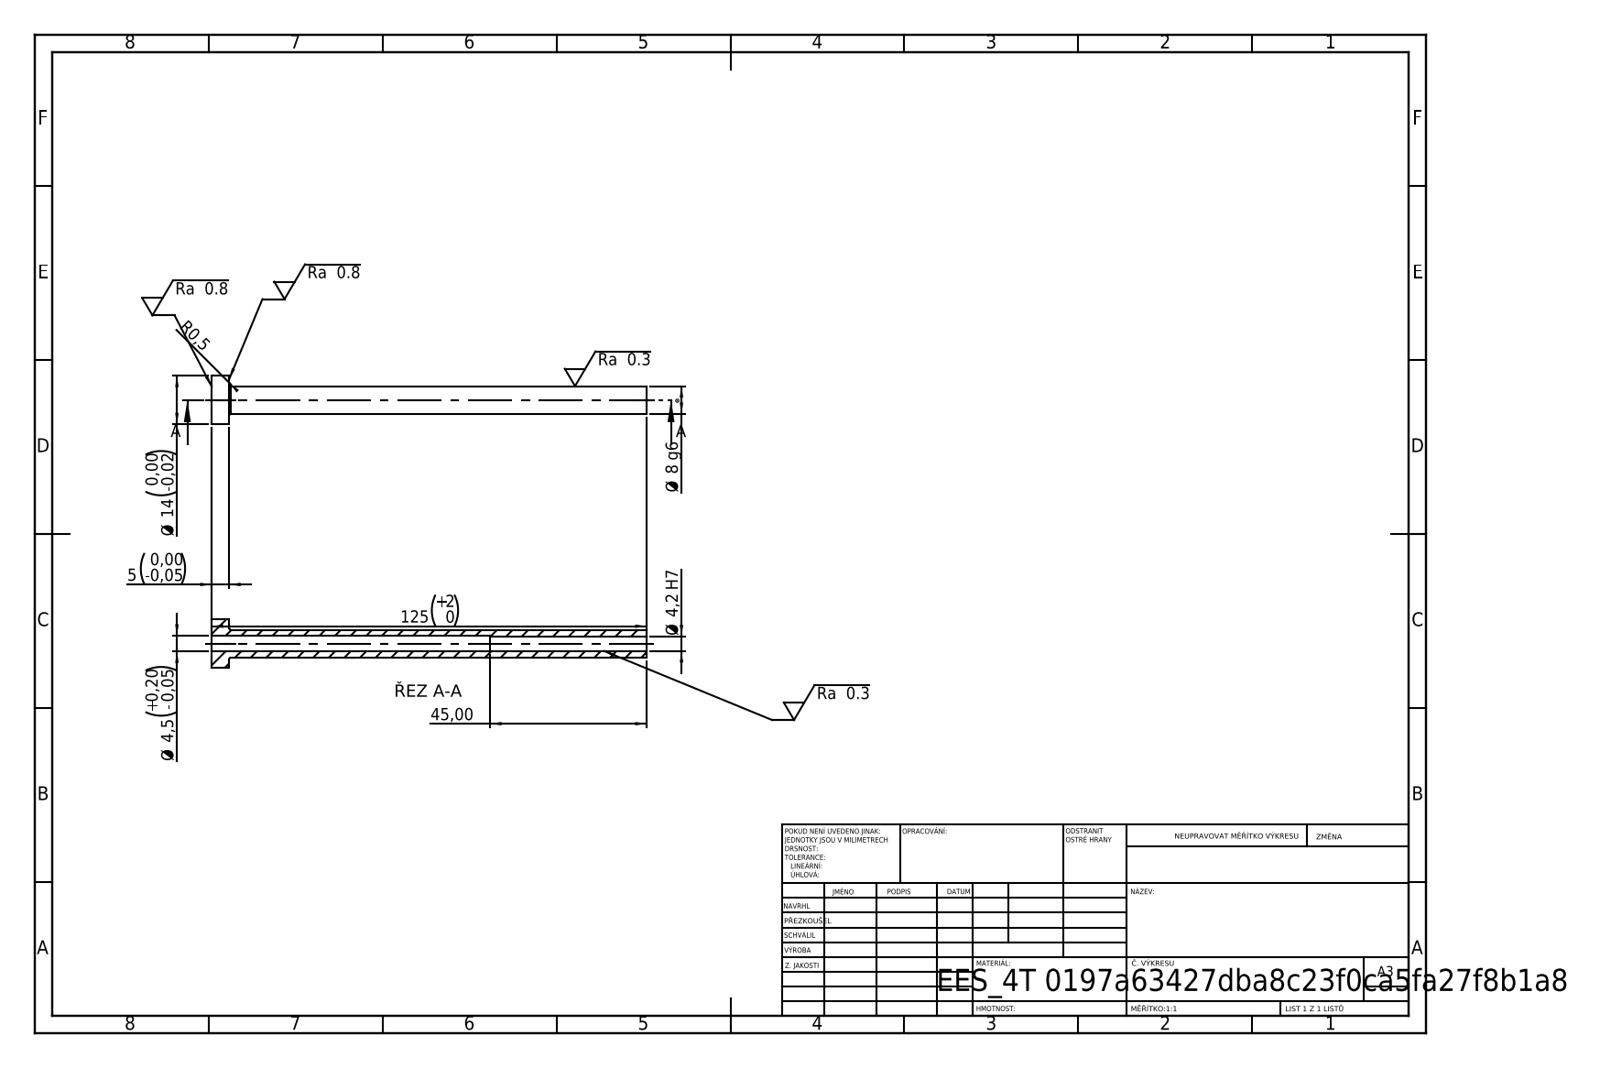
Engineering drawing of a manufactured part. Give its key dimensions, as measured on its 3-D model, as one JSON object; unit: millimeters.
{"step_written_by": "SolidWorks 2019 (CONFIG_CONTROL_DESIGN)", "units": "millimeters", "bodies": {"solids": 1, "faces": 14, "planar": 4, "cylindrical": 8, "other": 2}, "overall_size": [125, 14, 14], "volume_mm3": 4907, "surface_area_mm2": 5235, "round_holes": [[4.2, 1], [4.5, 1]], "round_bosses_or_shafts": [[14, 1], [8, 1]], "face_to_face_distances": [5, 125, 120, 80, 75, 45]}
